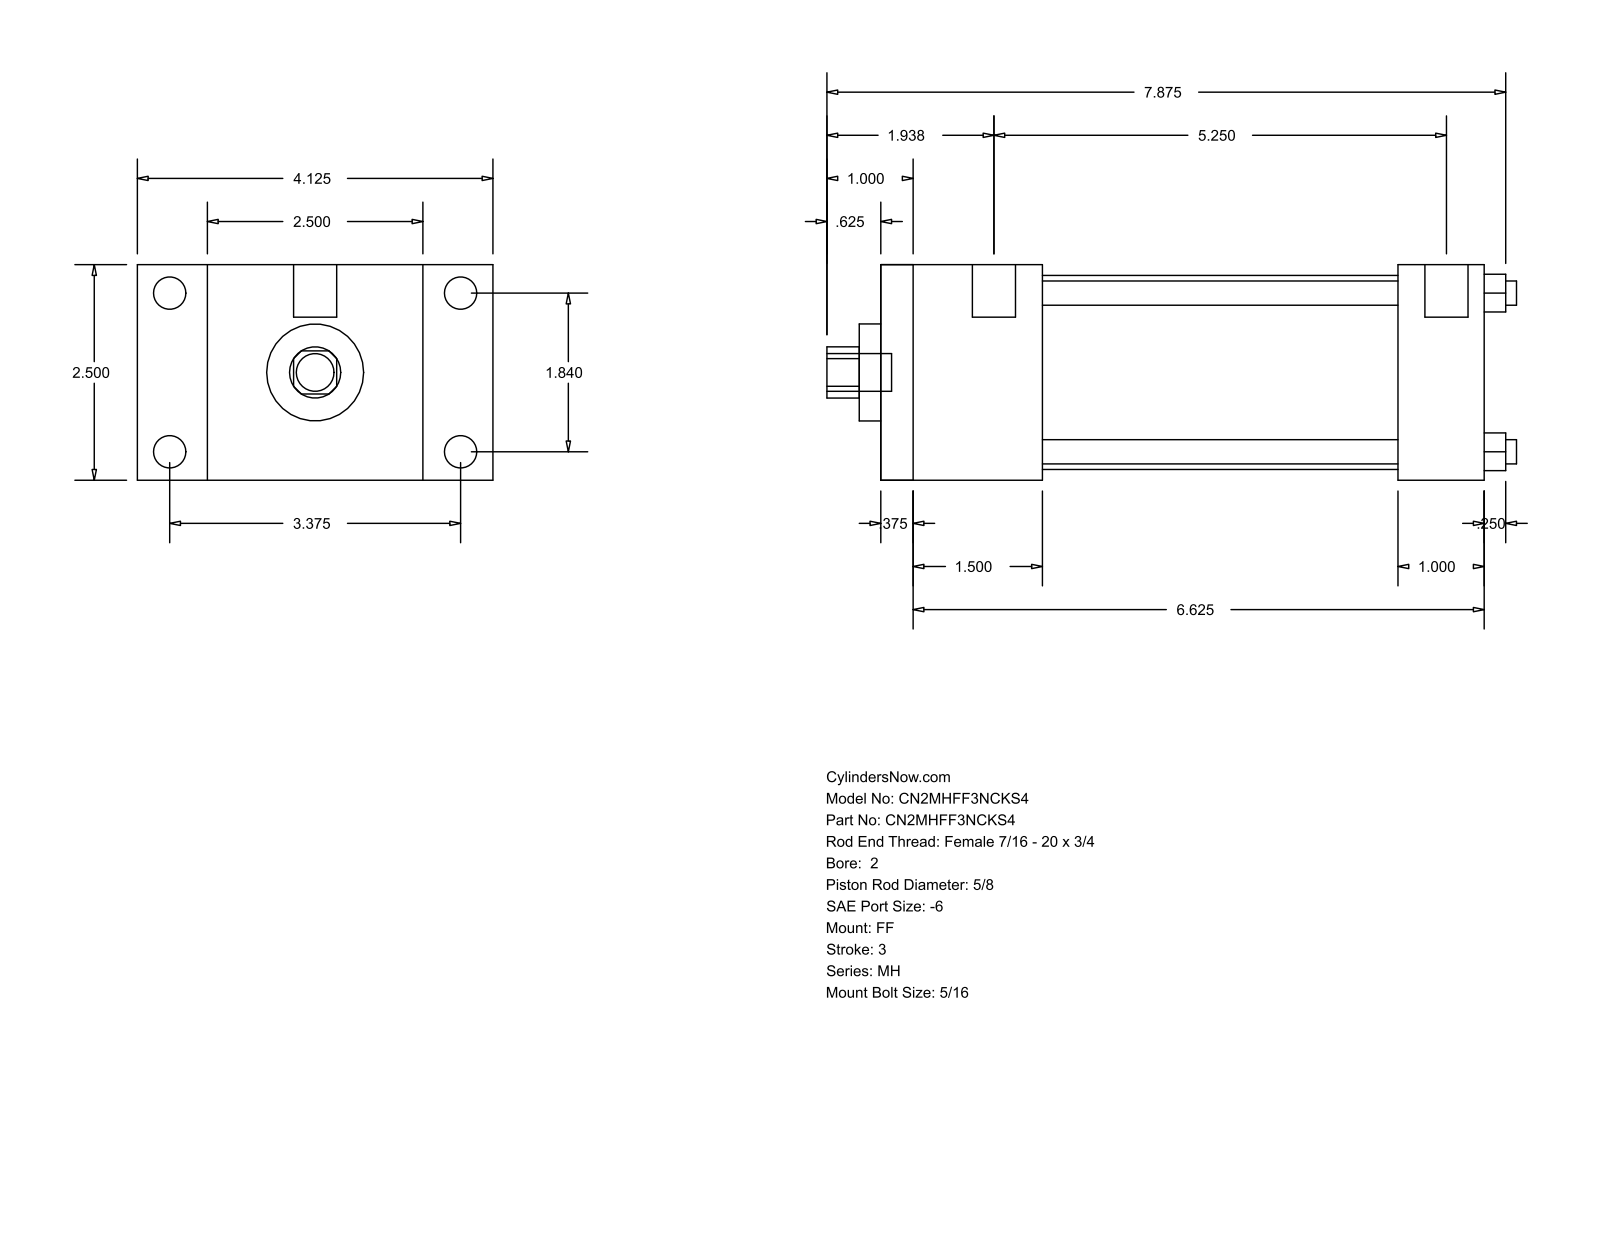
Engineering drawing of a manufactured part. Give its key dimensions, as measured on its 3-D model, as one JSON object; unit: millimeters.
{"part_name": "MH_FF__0200_0.625", "step_written_by": "GSSL Pune (CONFIG_CONTROL_DESIGN)", "units": "millimeters", "bodies": {"solids": 0, "faces": 92, "planar": 64, "cylindrical": 28, "other": 0}, "overall_size": [203.2, 104.78, 63.5], "round_holes": [[7.14, 4], [15.88, 1], [28.57, 1], [57.15, 1]], "round_bosses_or_shafts": [[9.53, 4], [5.56, 4], [12.7, 2], [11.11, 1]], "partial_cylinders_radius": [[7.54, 1]], "face_to_face_distances": [63.5, 177.8, 9.52, 168.28, 104.78, 25.4, 38.1, 47.62, 152.4, 142.88], "hole_center_spacings": [33.05, 46.74, 66.1]}
